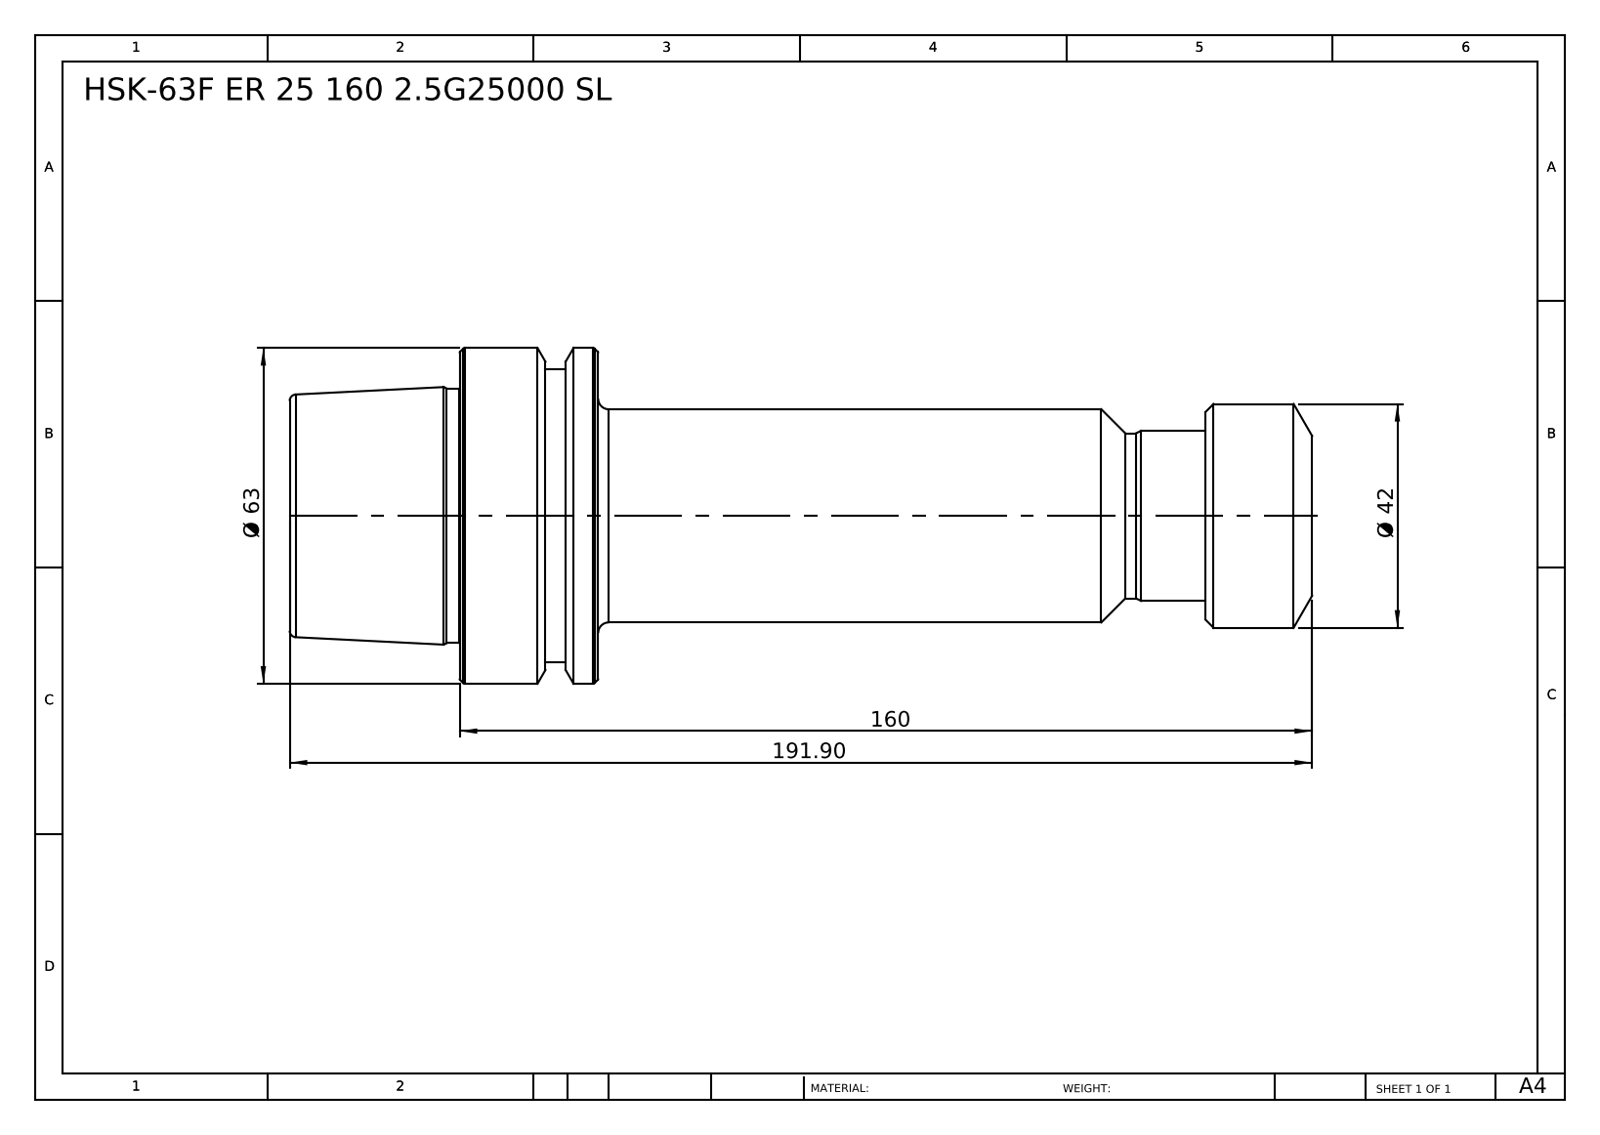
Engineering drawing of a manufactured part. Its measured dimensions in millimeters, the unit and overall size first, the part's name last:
Units: millimetres
Overall size (bounding box): 191.9 × 63 × 63
Round bosses / shafts (diameter × count): ⌀63 ×1, ⌀55 ×1, ⌀47.78 ×1, ⌀42 ×1, ⌀40 ×1, ⌀31.9 ×1, ⌀31 ×1
Main face-to-face distances: 57.9, 26, 31.9, 134, 160, 191.9, 20, 114, 140, 171.9
Volume: 294 086 mm³ · Surface area: 33 513 mm²
Bodies: 1 solid, 59 faces (7 planar, 16 cylindrical, 36 other)
Part name (STEP PRODUCT): HSK-A 63 ER 25 160 6.3G 20000 SL
STEP written by: SolidWorks 2014 (CONFIG_CONTROL_DESIGN)
